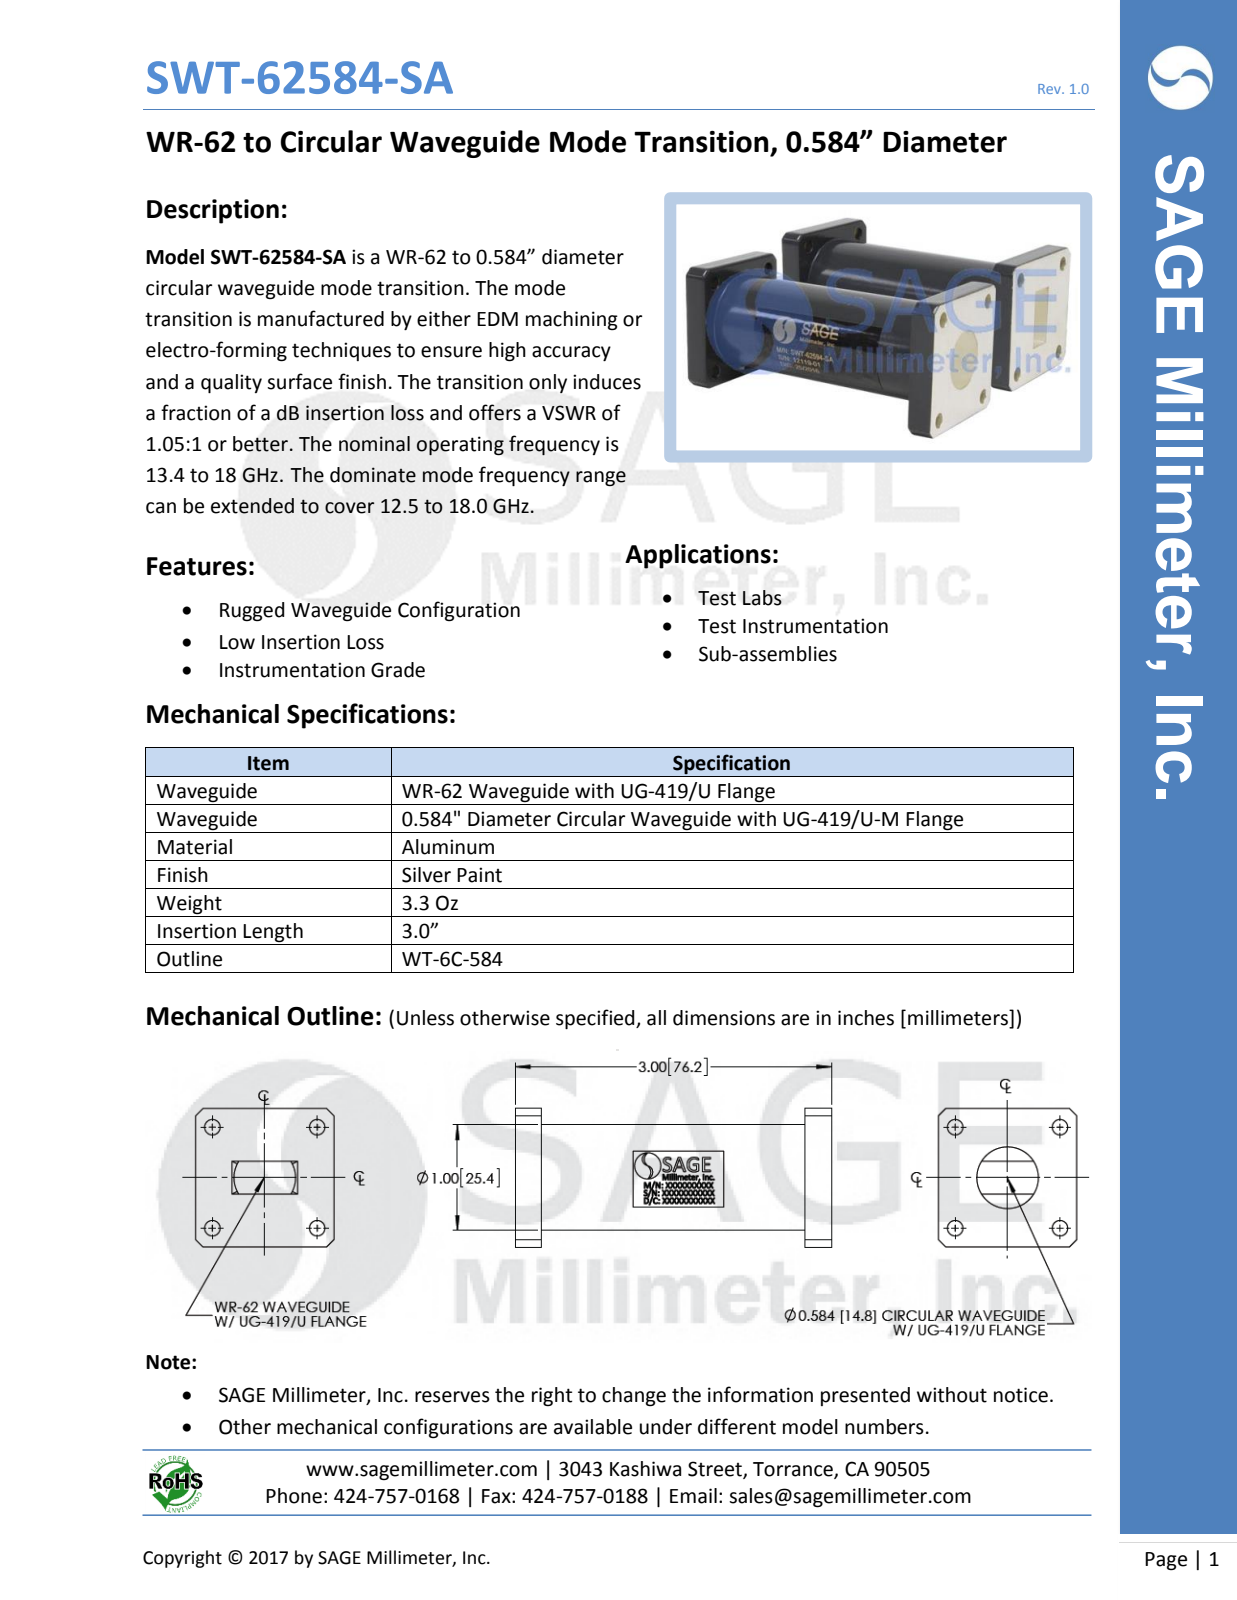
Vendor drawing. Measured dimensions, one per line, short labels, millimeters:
name: SWT-62584-SA
written by: SolidWorks 2016 (AUTOMOTIVE_DESIGN)
unit: mm
bodies: 1 solid, 46 faces (26 planar, 20 cylindrical, 0 other)
size: 76.2 × 33.3 × 33.3
volume: 45 640 mm³; area: 10 540 mm²
holes: 4× ⌀3.7, 1× ⌀14.8
bosses: 1× ⌀25.4
face distances: 6.4, 69.9, 76.2, 33.3, 63.5, 76.2, 6.3, 69.8, 76.1, 44.6
hole spacings: 17.5, 17.5, 24.3, 25.2, 35
